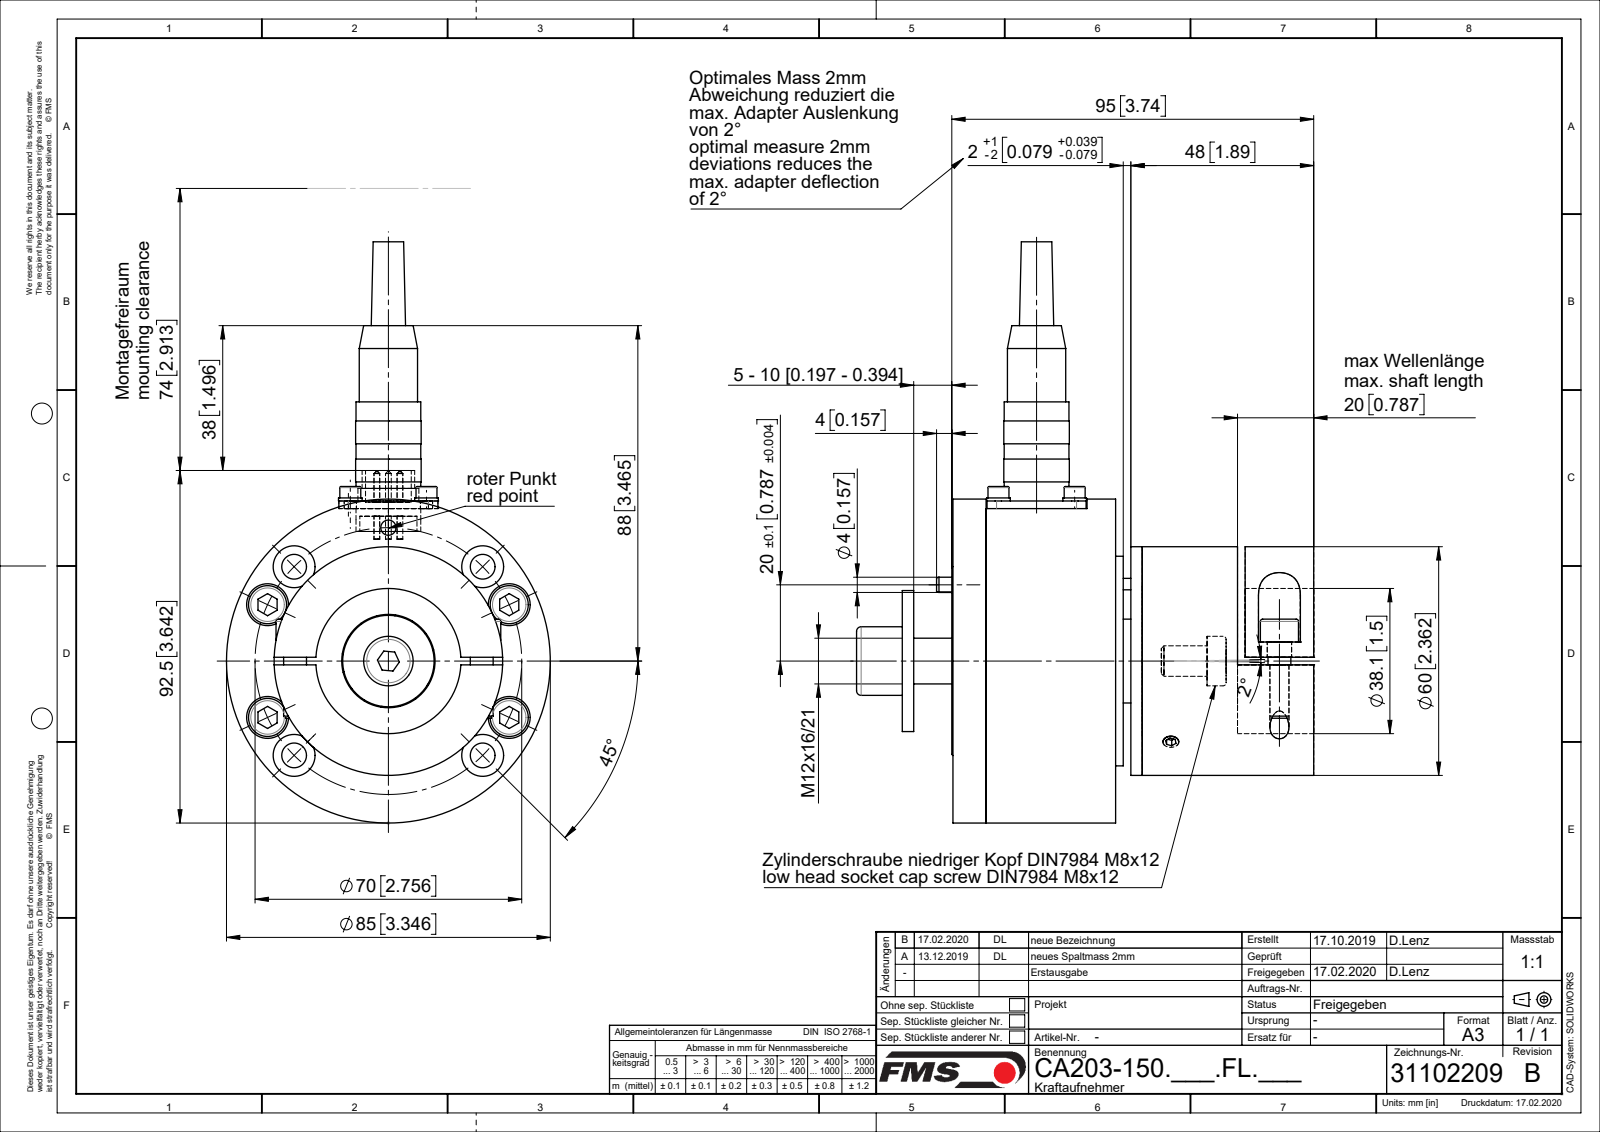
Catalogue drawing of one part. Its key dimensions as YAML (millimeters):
part_name: "C0709101_DI150; C0709081; C0612056; C0709072 (+8 more)"
step_written_by: "Mechanical Desktop 2009 (CONFIG_CONTROL_DESIGN)"
units: millimeters
bodies: {solids: 38, faces: 698, planar: 225, cylindrical: 333, other: 140}
overall_size: [152.5, 120.5, 85]
volume: 325598
surface_area: 119806
round_holes:
  - {diameter: 2.6, count: 8}
  - {diameter: 6.5, count: 8}
  - {diameter: 11, count: 8}
  - {diameter: 5.15, count: 6}
  - {diameter: 7, count: 5}
  - {diameter: 3.2, count: 4}
  - {diameter: 3.6, count: 4}
  - {diameter: 4, count: 4}
  - {diameter: 6.4, count: 2}
  - {diameter: 3, count: 1}
  - {diameter: 4.33, count: 1}
  - {diameter: 7.15, count: 1}
round_bosses_or_shafts:
  - {diameter: 6, count: 10}
  - {diameter: 3, count: 8}
  - {diameter: 10, count: 6}
  - {diameter: 1.5, count: 5}
  - {diameter: 6.2, count: 4}
  - {diameter: 5.5, count: 4}
  - {diameter: 5, count: 4}
  - {diameter: 85, count: 1}
partial_cylinders:
  - {radius: 2.5, count: 4}
  - {radius: 5, count: 4}
  - {radius: 5.5, count: 2}
face_to_face_distances: [45, 49.5, 6, 3, 46.5, 9, 11.5, 2, 31.5, 10]
hole_center_spacings: [24.78, 25.2, 56.46, 20, 32.8, 35, 51.14, 28.28]
